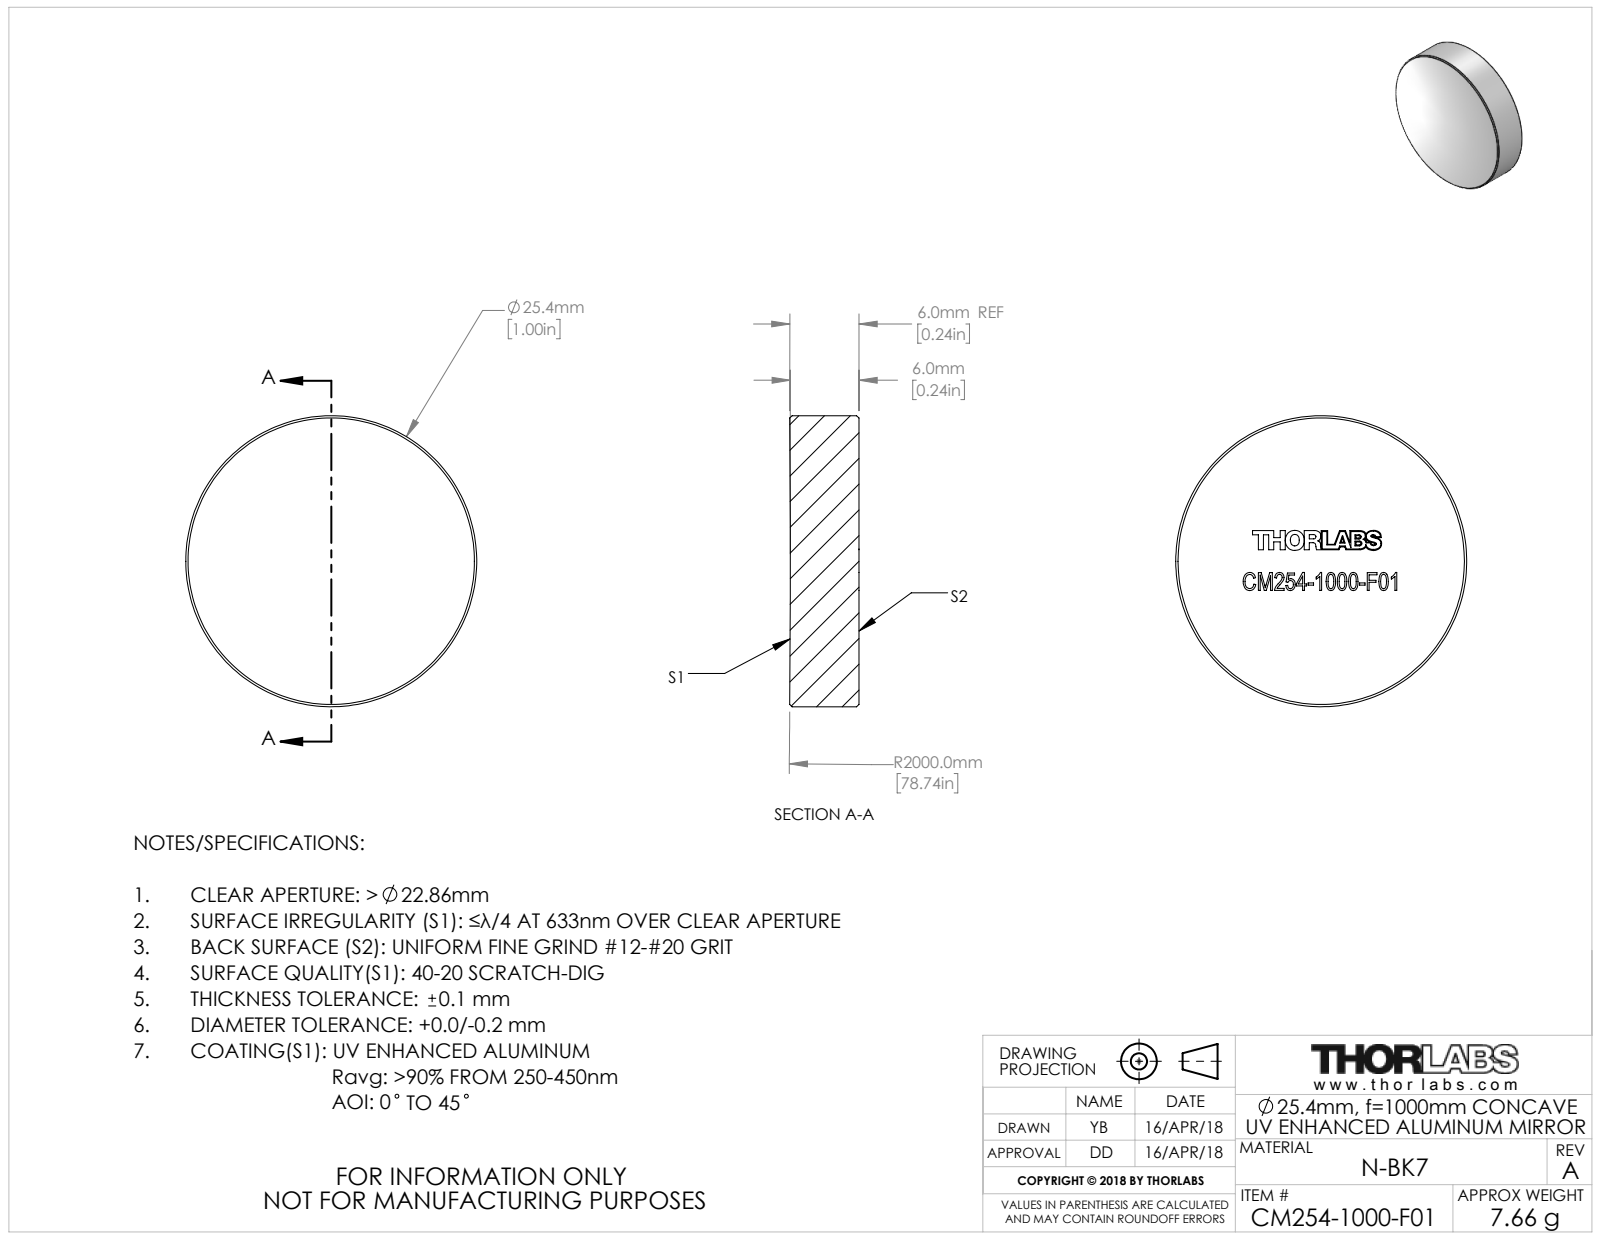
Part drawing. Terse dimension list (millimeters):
name: TTN153313-E0W
written by: SolidWorks 2018 (CONFIG_CONTROL_DESIGN)
unit: mm
bodies: 1 solid, 43 faces (35 planar, 2 cylindrical, 6 other)
size: 25.4 × 25.4 × 6.04
volume: 3 047 mm³; area: 1 477 mm²
bosses: 1× ⌀25.4
